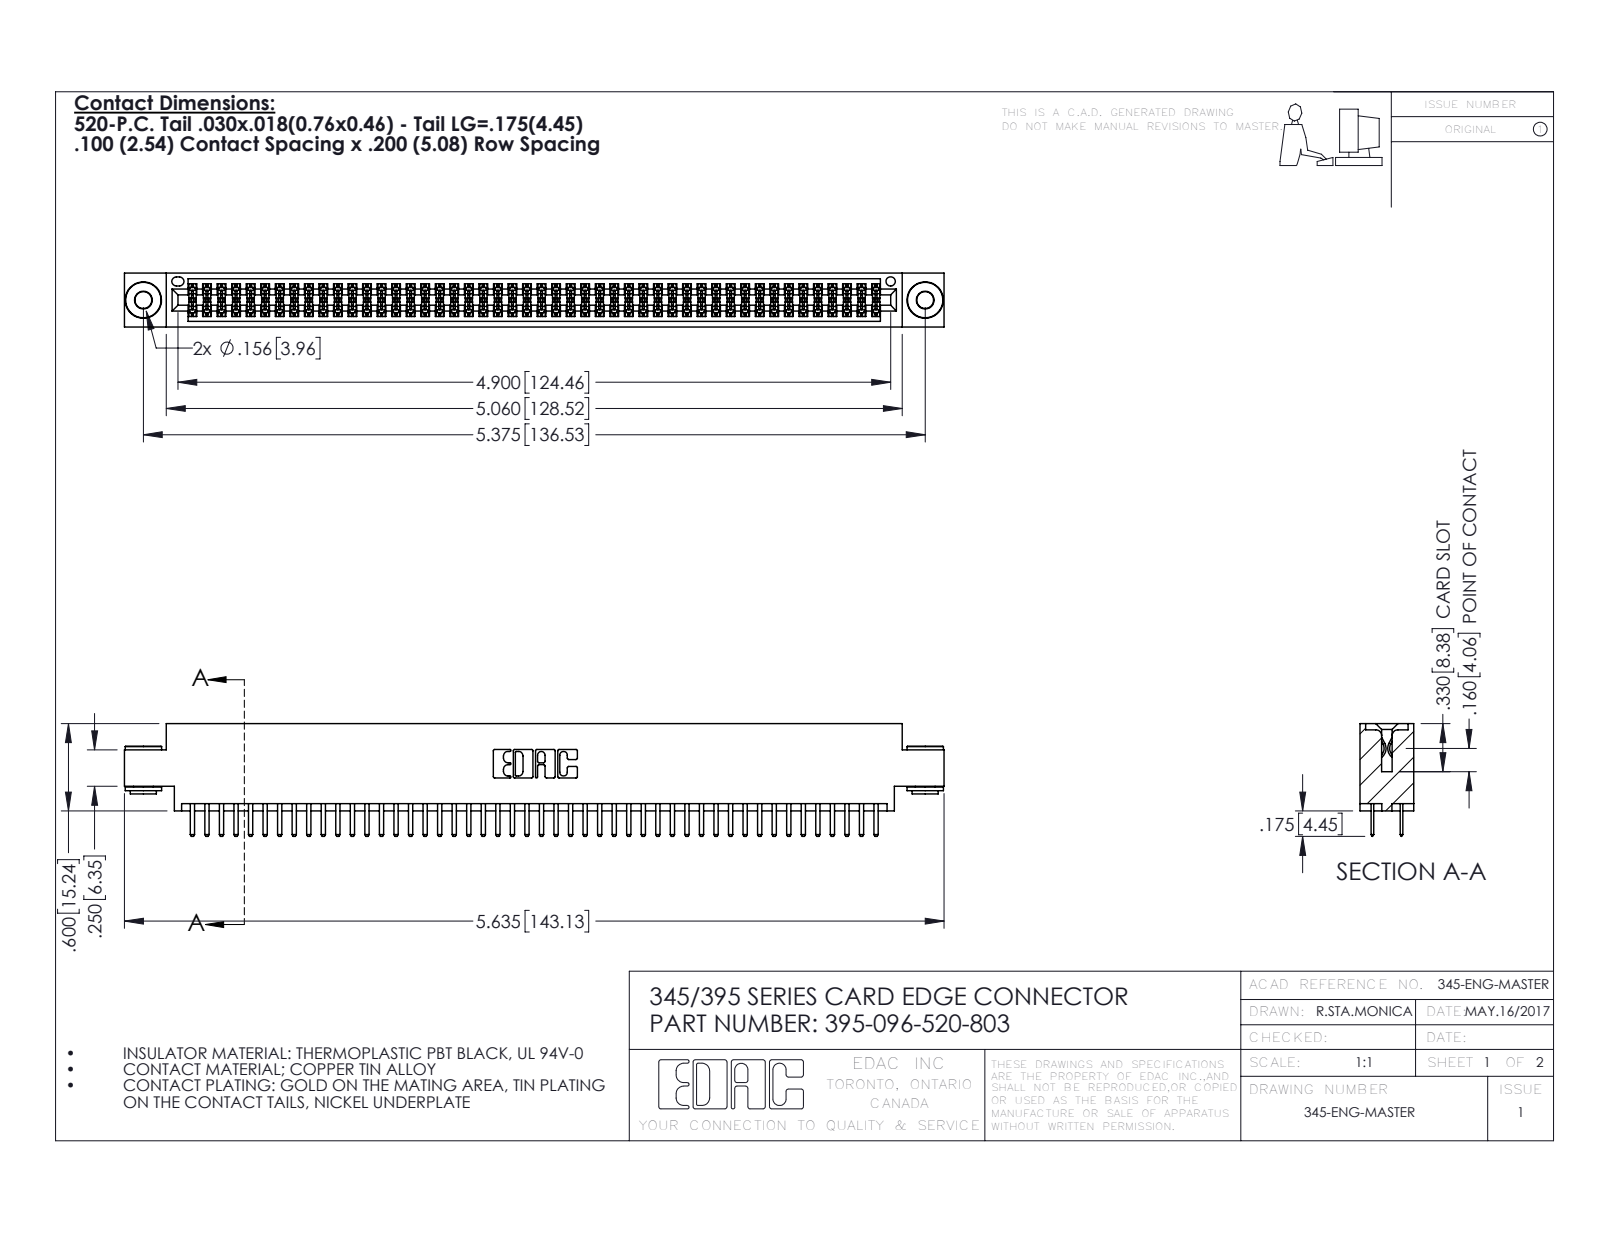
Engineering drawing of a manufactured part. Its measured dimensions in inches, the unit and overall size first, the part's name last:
Units: inches
Overall size (bounding box): 5.635 × 0.775 × 0.37
Round holes (diameter × count): ⌀0.116 ×2, ⌀0.156 ×2, ⌀0.064 ×1
Round bosses / shafts (diameter × count): ⌀0.25 ×2, ⌀0.18 ×2, ⌀0.136 ×2
Partial cylindrical surfaces — rounded edges, fillets, slot ends (radius × count): R0.006 ×144, R0.01 ×100, R0.01 ×22, R0.007 ×6, R0.031 ×6, R0.026 ×3, R0.014 ×2, R0.019 ×2
Main face-to-face distances: 0.072, 0.298, 0.2, 0.37, 0.098, 0.272, 0.025, 0.225, 0.022, 0.175
Hole centre spacings: 0.27, 5.139, 5.375
Volume: 0.844 in³ · Surface area: 32.25 in²
Bodies: 99 solids, 5352 faces (3454 planar, 1890 cylindrical, 8 other)
Part name (STEP PRODUCT): 395-096-520-803; 345 Part_0.170 Offset - 0.156 Dia-TH; 345-250-002_345-250-002-102; 345-292-001_345-293-120
STEP written by: SolidWorks 2016 (CONFIG_CONTROL_DESIGN)
